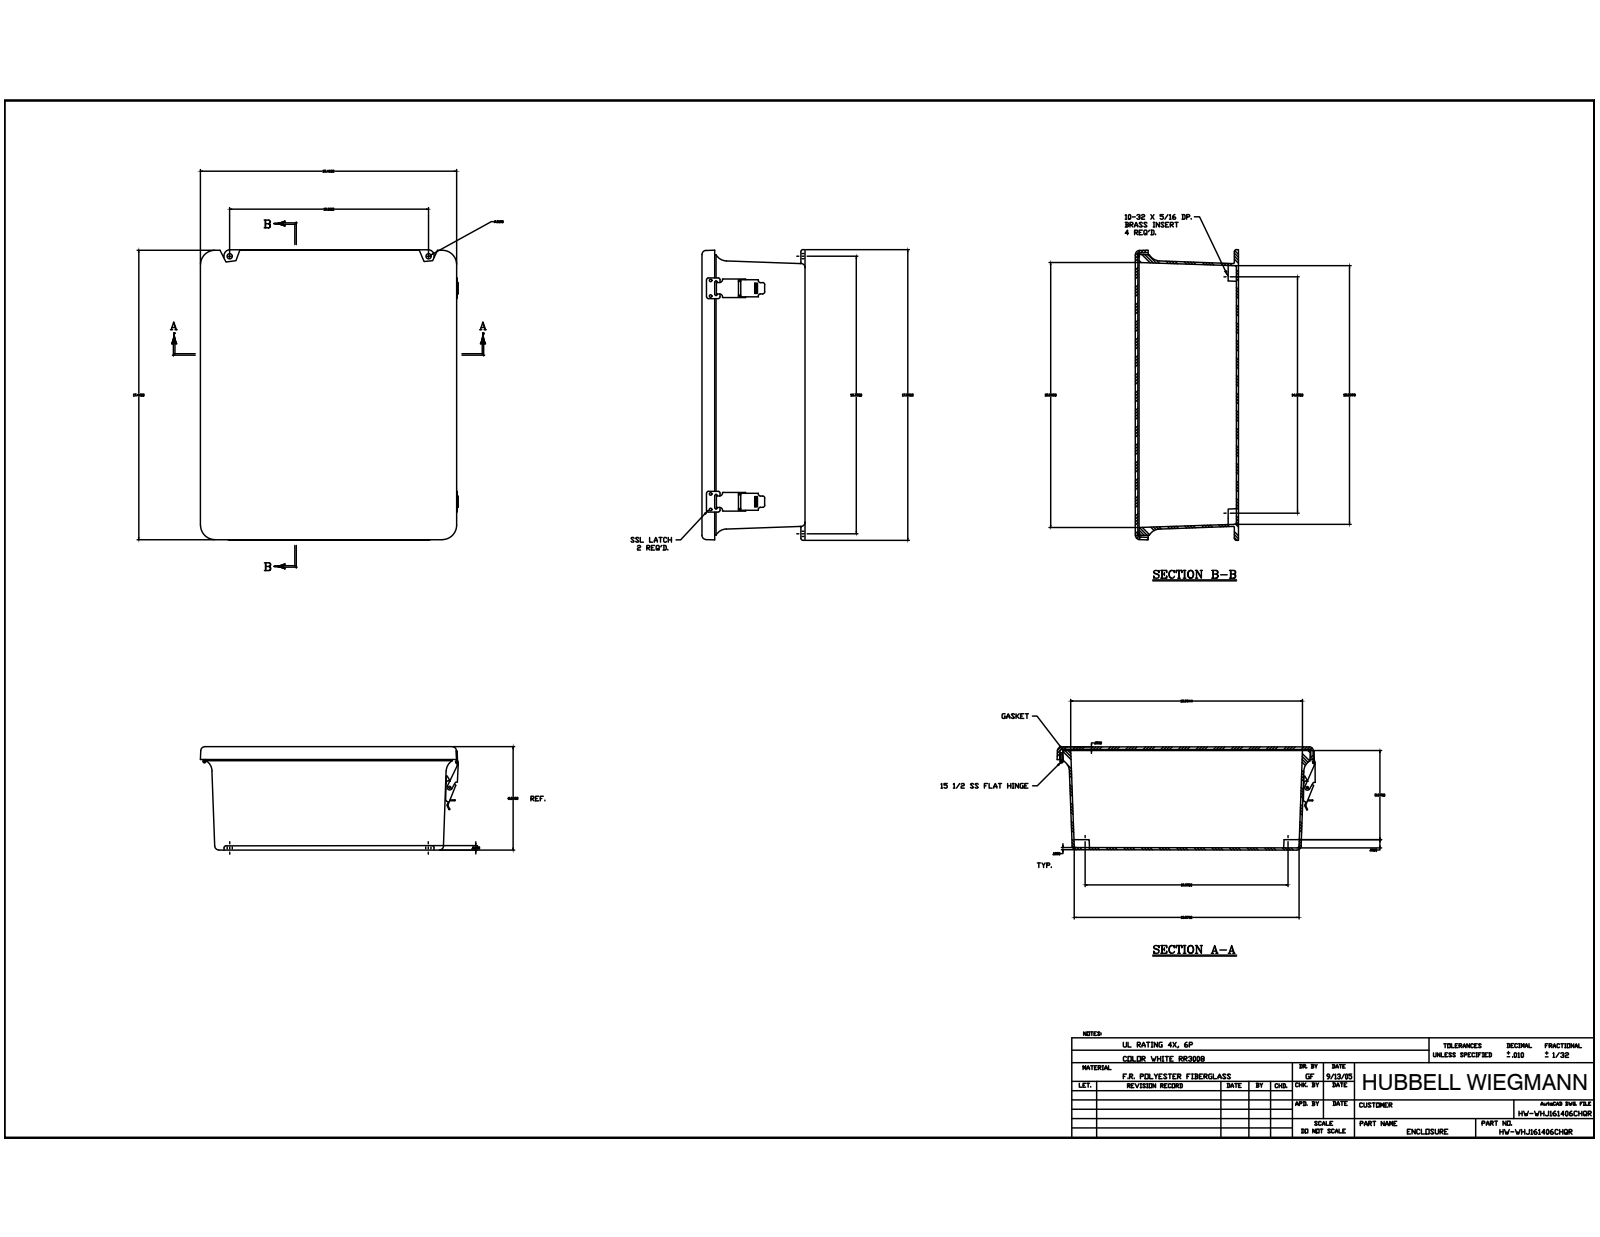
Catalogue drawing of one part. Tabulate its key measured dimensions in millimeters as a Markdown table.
| quantity | value |
| --- | --- |
| part name | J1614HL_2; RMINS45821P_49; RMINS45821P_50; RMINS45821P_51 (+8 more) |
| STEP written by | Autodesk Inventor 2014 (AUTOMOTIVE_DESIGN) |
| units | millimeters |
| bodies | 40 solids, 1086 faces (481 planar, 456 cylindrical, 149 other) |
| overall size | 445.29 × 396.13 × 158.03 |
| volume | 2 364 000 mm³ |
| surface area | 1 270 000 mm² |
| round holes (diameter × count) | 3.56 × 22, 3.33 × 10, 2.64 × 8, 3.86 × 8, 3.3 × 4, 3.96 × 4, 5.54 × 4, 3.43 × 2, 9.52 × 2, 2.16 × 1 |
| round bosses / shafts (diameter × count) | 3.17 × 18, 6.35 × 10, 6.86 × 4, 7.62 × 1, 4.31 × 1, 3.94 × 1, 3.05 × 1 |
| partial cylindrical surfaces (radius × count) | 0.38 × 20, 0.79 × 20, 3.17 × 20, 1.14 × 16, 0.76 × 12, 6.35 × 12, 0.57 × 9, 1.52 × 6 |
| main face-to-face distances | 3.18, 3.86, 154.17, 158.03, 150.99, 154.85, 3.17, 152.4, 149.22, 1.77 |
| hole center spacings | 95.25, 190.5, 326.86, 23.81, 326.84, 6.35, 19.05, 285.75 |
